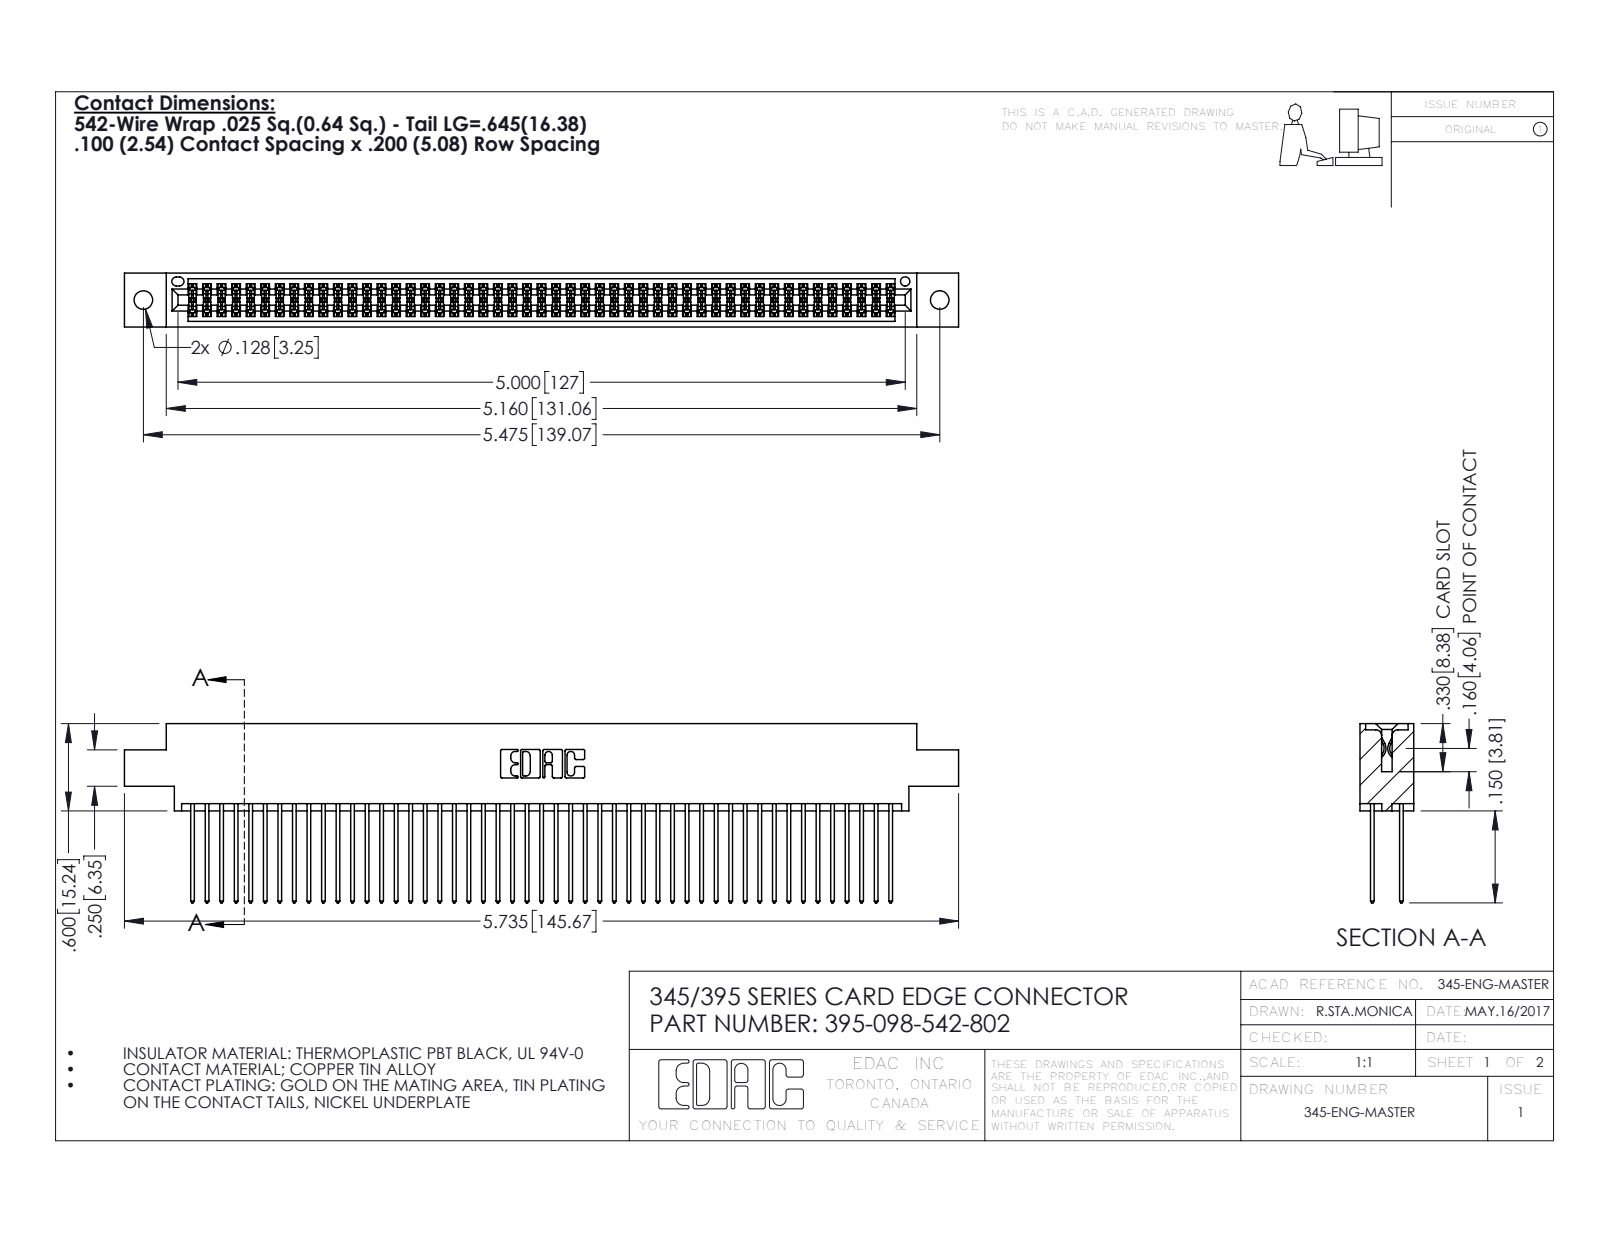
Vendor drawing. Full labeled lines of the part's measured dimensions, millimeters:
Part name (STEP PRODUCT): 395-098-542-802; 345-292-001_345-293-142; 345 Part_0.170 Offset - 0.128 Dia
STEP written by: SolidWorks 2016 (CONFIG_CONTROL_DESIGN)
Units: millimetres
Bodies: 99 solids, 5030 faces (3318 planar, 1712 cylindrical, 0 other)
Overall size (bounding box): 145.7 × 31.3 × 9.4
Volume: 14 500 mm³ · Surface area: 23 610 mm²
Round holes (diameter × count): ⌀3.3 ×2, ⌀1.6 ×1
Partial cylindrical surfaces — rounded edges, fillets, slot ends (radius × count): R0.2 ×147, R0.3 ×98, R0.3 ×22, R0.2 ×6, R0.8 ×6, R0.7 ×3, R0.4 ×2, R0.5 ×2
Main face-to-face distances: 1.8, 7.6, 5.1, 2.5, 6.9, 0.6, 9.4, 5.7, 4.4, 3.8
Hole centre spacings: 6.9, 133.1, 139.1
